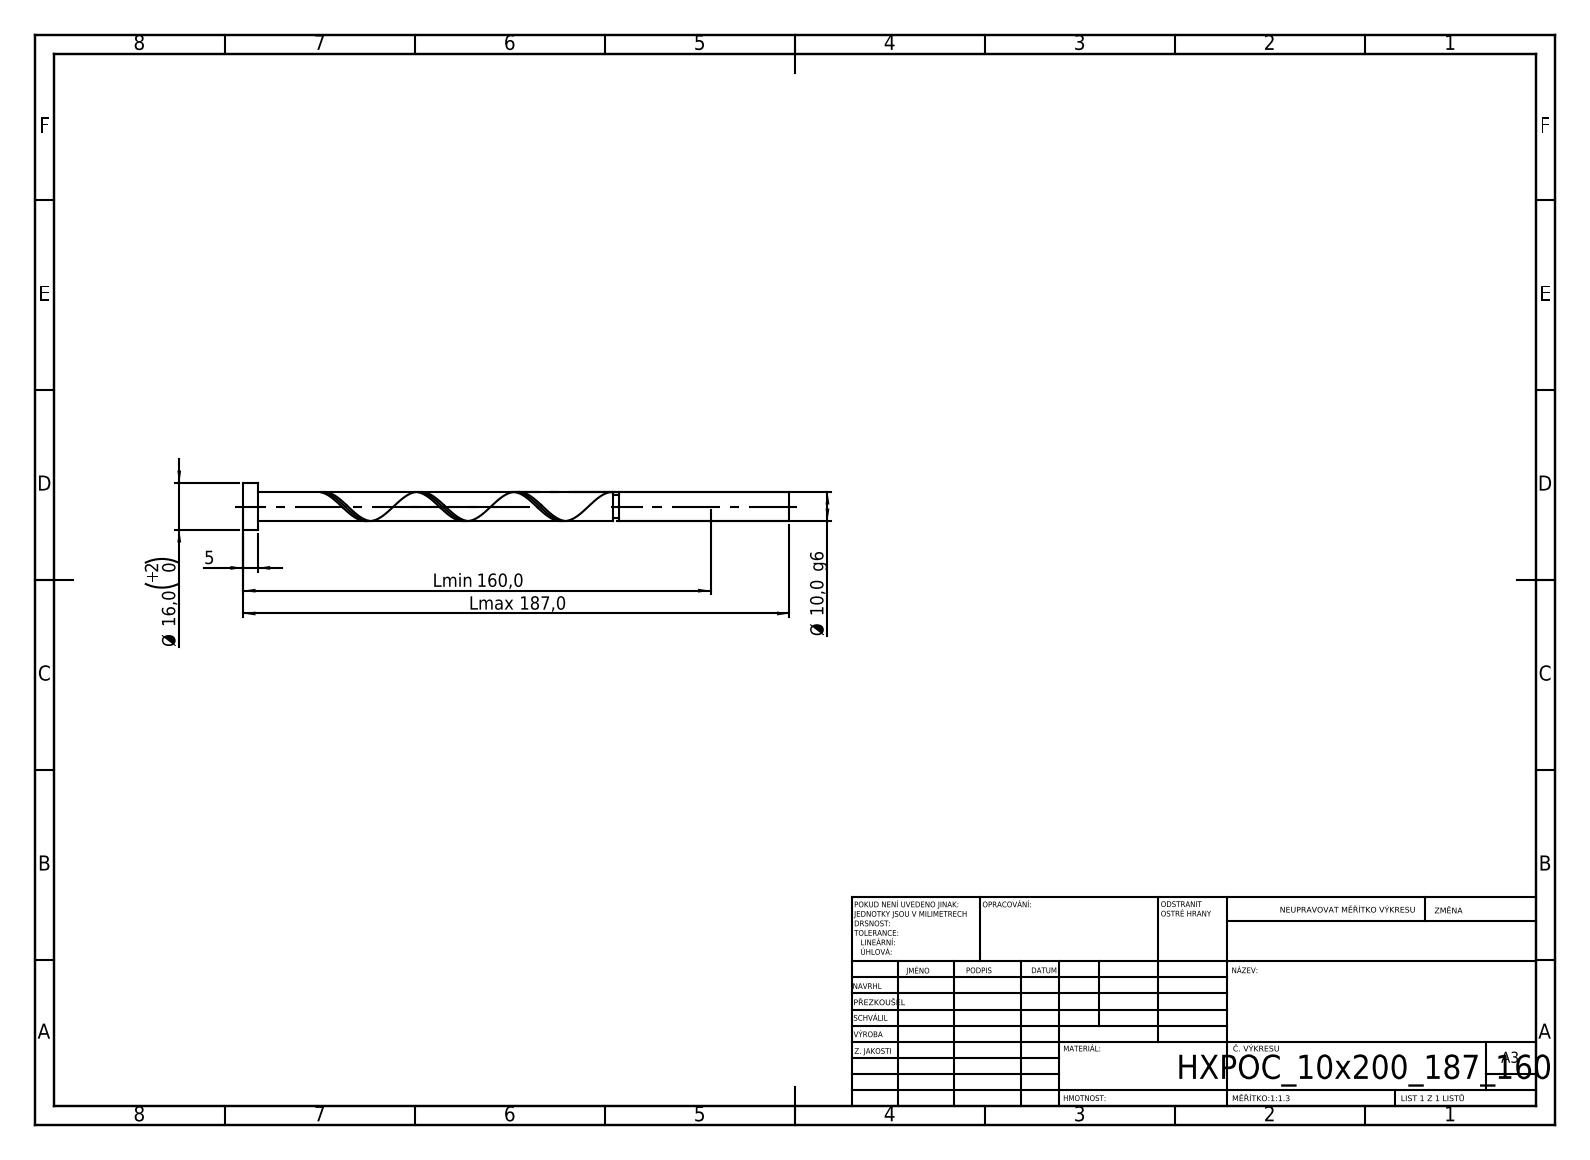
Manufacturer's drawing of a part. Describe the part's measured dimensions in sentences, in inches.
Its 3-D file was written by "SolidWorks 2019 (CONFIG_CONTROL_DESIGN)". It is 1 solid with 21 faces: 6 planar, 14 cylindrical and 1 other. Overall it measures 7.362 by 0.63 by 0.63 inches. Its volume is 0.921 cubic inches and its surface area 10.17 square inches. Round bosses or shafts: 1 of diameter 0.63, 1 of diameter 0.394, 1 of diameter 0.315. The main face-to-face distances are 0.197, 7.362, 7.165, 5.06, 4.863, 2.302, 4.981, 4.785, 0.079, 2.381.
